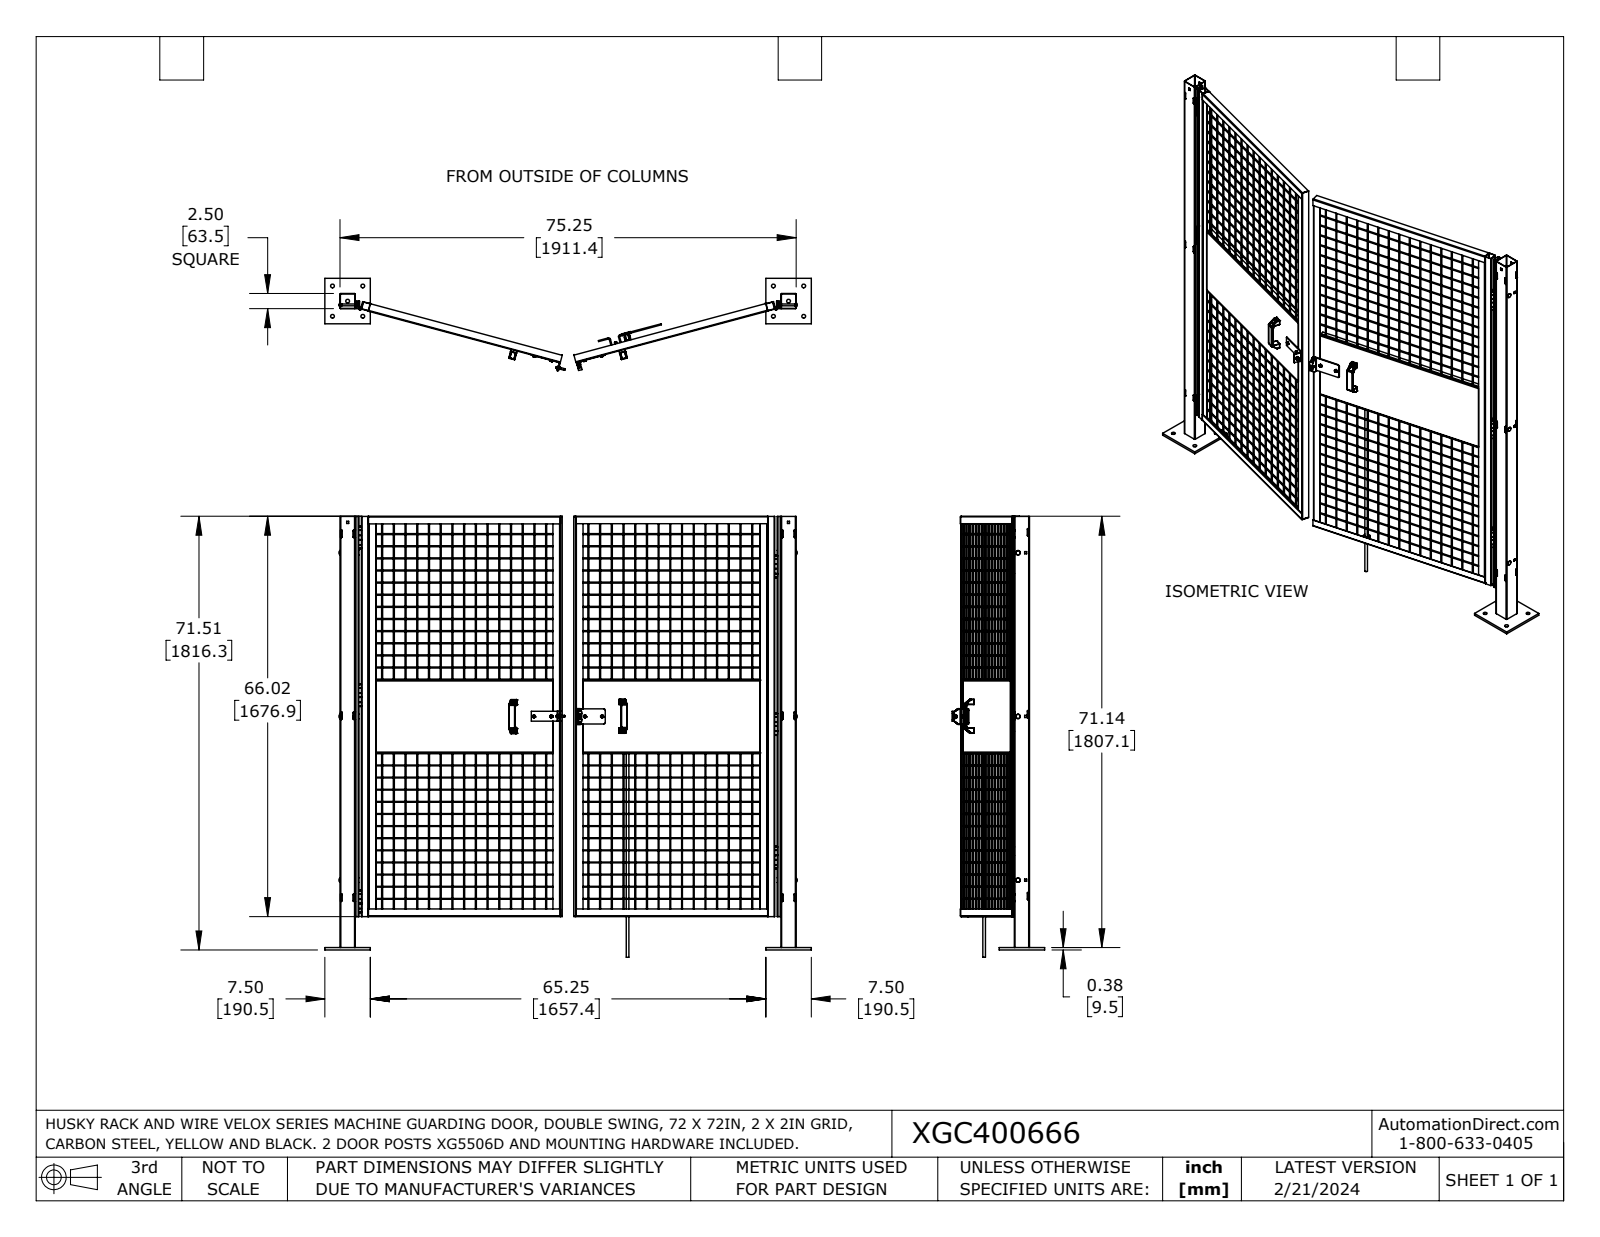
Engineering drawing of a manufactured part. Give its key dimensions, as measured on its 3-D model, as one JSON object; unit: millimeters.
{"part_name": "XGC400666", "step_written_by": "SolidWorks 2023 (AUTOMOTIVE_DESIGN)", "units": "millimeters", "bodies": {"solids": 87, "faces": 2570, "planar": 1463, "cylindrical": 717, "other": 390}, "overall_size": [2038.4, 1847.5, 387.7], "volume_mm3": 6717000, "surface_area_mm2": 6965000, "round_holes": [[9.1, 12], [6.4, 11], [12.7, 10], [15.9, 10], [4.6, 8], [6.1, 6], [6, 4], [3.5, 2], [4.3, 2], [4.7, 1], [7.4, 1], [9.5, 1]], "round_bosses_or_shafts": [[4.2, 56], [4.1, 34], [15.1, 8], [6.4, 8], [17.4, 6], [8.1, 6], [38.1, 2], [11.1, 2]], "partial_cylinders_radius": [[1.3, 56], [0.2, 48], [3.3, 31], [1.6, 24], [0.6, 20], [3.2, 17], [1.6, 14], [3, 14]], "face_to_face_distances": [1.5, 62, 1.8, 1.8, 63.5, 1847.9, 60.6, 30.2, 1.5, 31.8], "hole_center_spacings": [89.8, 127, 1847.9, 179.6, 685.8, 685.8, 1371.6, 1785.5]}
